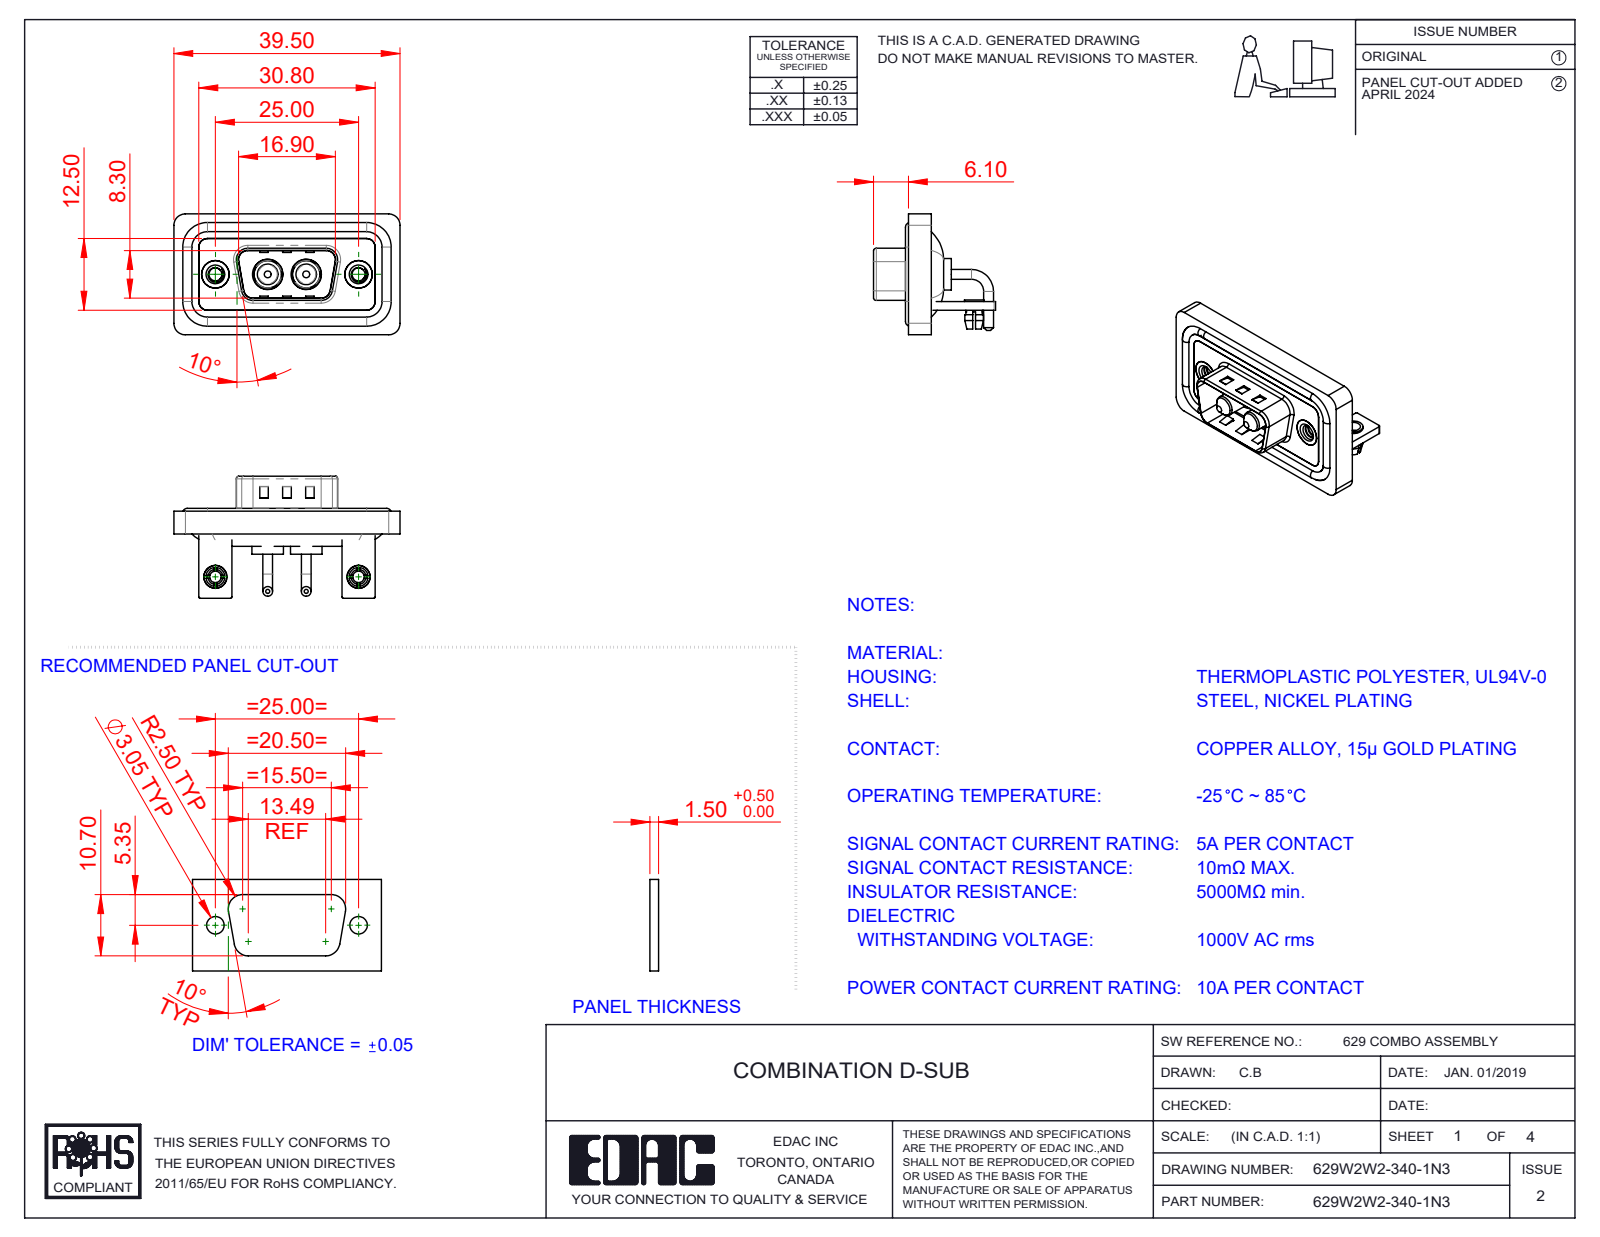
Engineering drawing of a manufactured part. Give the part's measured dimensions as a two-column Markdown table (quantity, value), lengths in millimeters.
| quantity | value |
| --- | --- |
| part name | 629Combo Shell Rear_09 Contacts; 629Combo Stabilizer Bracket; 629Combo Shell Front_09 Contacts; 629Combo Threaded Rivet_3 (+5 more) |
| STEP written by | SolidWorks 2023 (CONFIG_CONTROL_DESIGN) |
| units | millimeters |
| bodies | 15 solids, 629 faces (233 planar, 272 cylindrical, 124 other) |
| overall size | 39.5 × 21.3 × 21.1 |
| volume | 4 782 mm³ |
| surface area | 7 863 mm² |
| round holes (diameter × count) | 2 × 2, 2.26 × 2, 2.5 × 2, 3.2 × 2, 4 × 2, 4.8 × 2, 4.85 × 2, 5 × 2, 5.3 × 2 |
| round bosses / shafts (diameter × count) | 1.7 × 4, 1.6 × 4, 5.5 × 2, 5.2 × 2, 4.9 × 2, 4.75 × 2, 4 × 2, 3.75 × 2 |
| partial cylindrical surfaces (radius × count) | 2 × 19, 1.5 × 18, 0.25 × 16, 0.5 × 9, 1.6 × 8, 0.6 × 4, 0.65 × 4, 0.9 × 4 |
| main face-to-face distances | 0.4, 1.5, 2.9, 0.8, 1.1, 1.2, 2.1, 1.6, 3.7, 2.5 |
| hole center spacings | 9.14, 15.86, 25, 6.72 |
